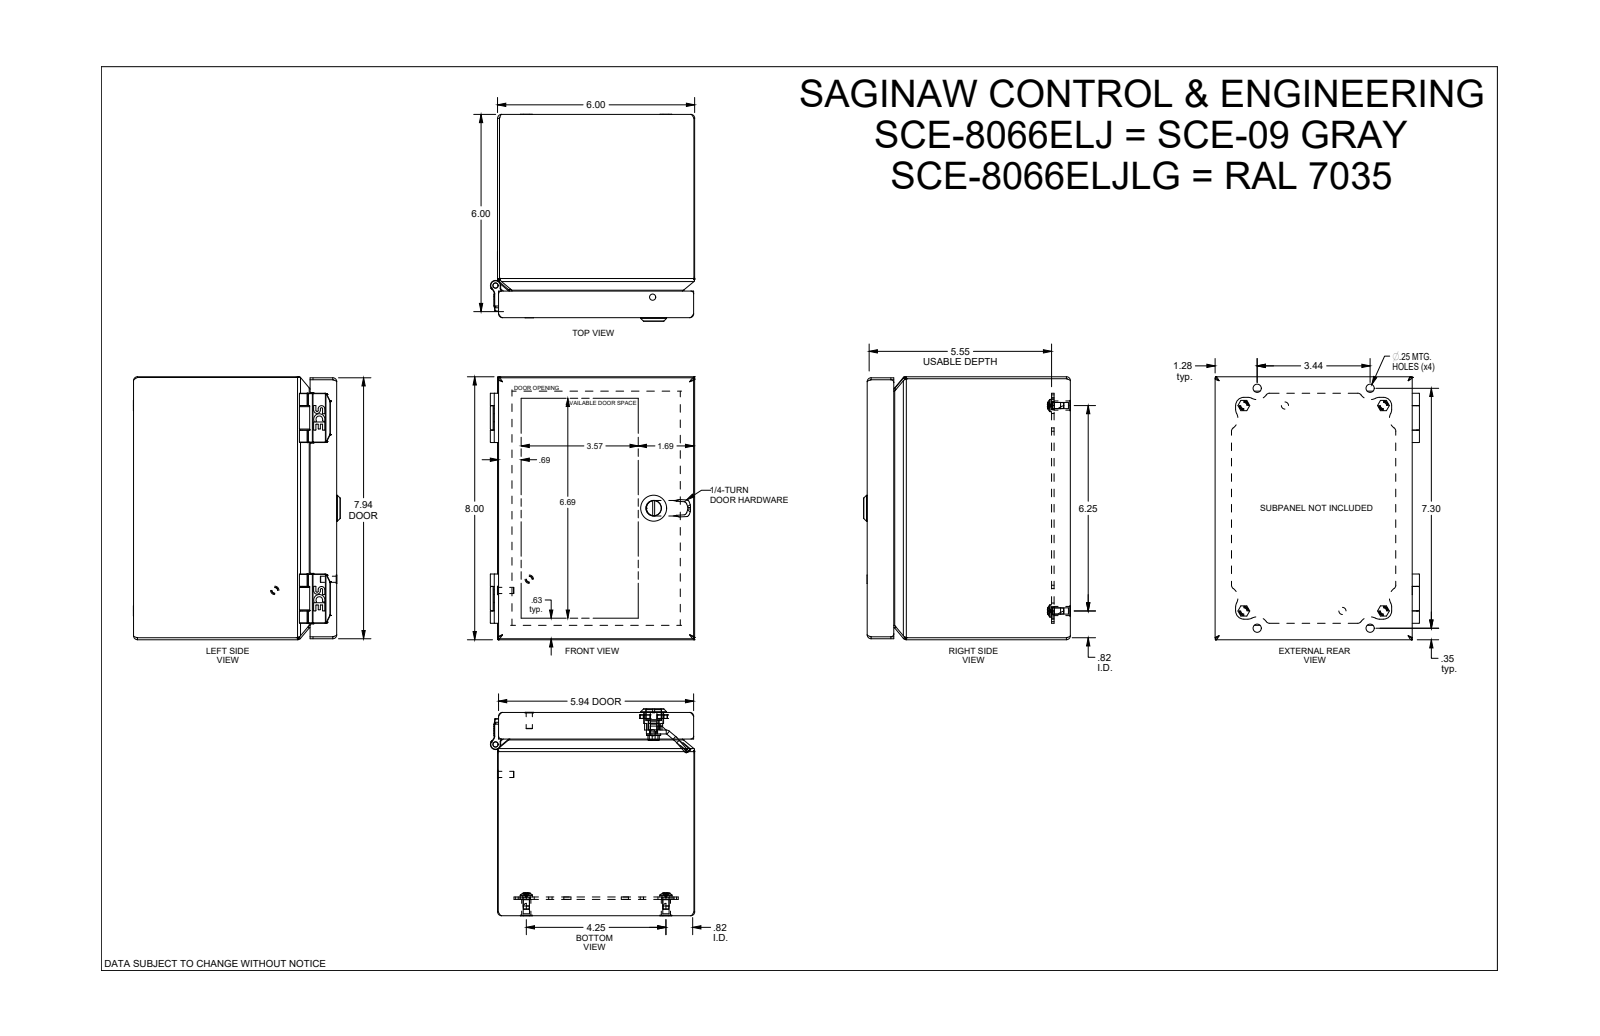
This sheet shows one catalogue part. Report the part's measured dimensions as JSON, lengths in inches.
{"part_name": "SCE-8066ELJ", "step_written_by": "SolidWorks 2021 (AUTOMOTIVE_DESIGN)", "units": "inches", "bodies": {"solids": 22, "faces": 1294, "planar": 401, "cylindrical": 390, "other": 503}, "overall_size": [8, 6.292, 6.22], "volume_in3": 20.13, "surface_area_in2": 654.8, "round_holes": [[0.25, 8], [0.284, 4], [0.17, 2], [0.218, 2], [0.158, 1], [0.2, 1], [0.239, 1], [0.254, 1], [0.269, 1], [0.282, 1], [0.326, 1], [0.475, 1]], "round_bosses_or_shafts": [[0.188, 5], [0.373, 4], [0.284, 4], [0.479, 2], [0.26, 2], [0.1, 2], [0.02, 2], [0.788, 1]], "partial_cylinders_radius": [[0.106, 66], [0.005, 36], [0.008, 32], [0.013, 21], [0.05, 16], [0.025, 12], [0.25, 12], [0.01, 10]], "face_to_face_distances": [0.059, 5.941, 0.062, 7.941, 6.123, 6.185, 6.126, 6.064, 6, 5.882], "hole_center_spacings": [3.88, 4.25, 6.25, 6.251, 6.787, 7.558, 7.789, 6.933]}
